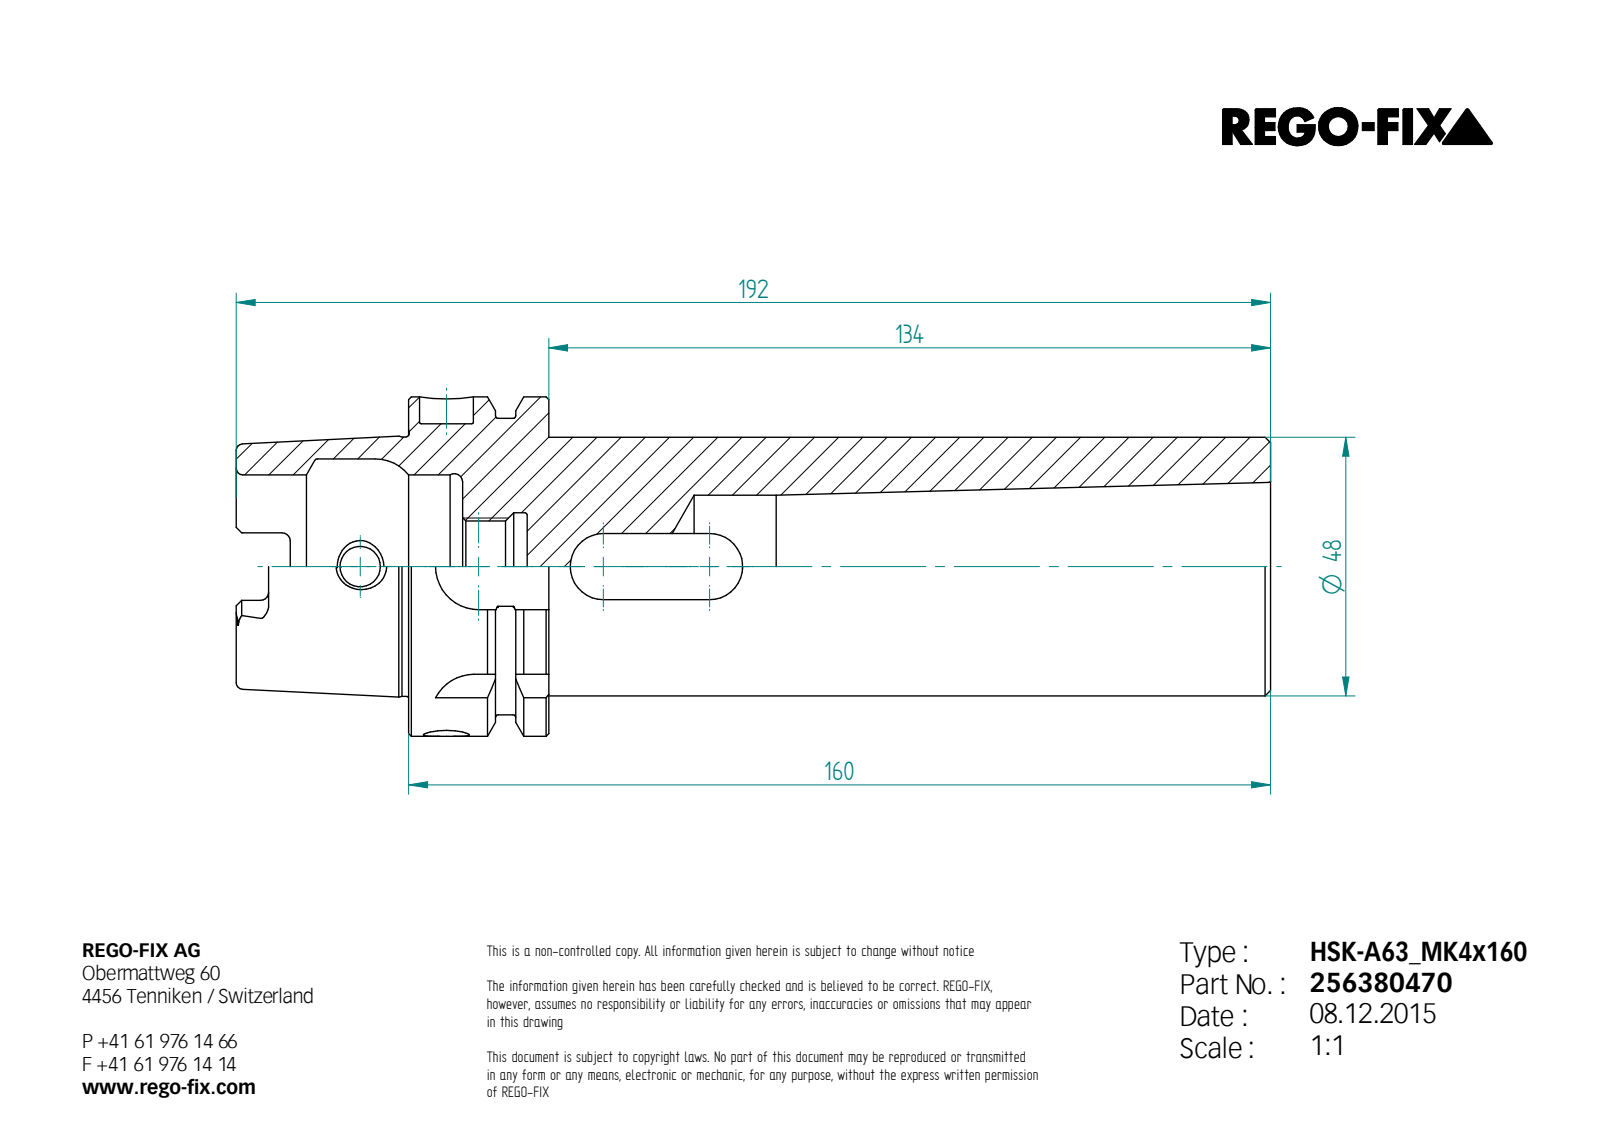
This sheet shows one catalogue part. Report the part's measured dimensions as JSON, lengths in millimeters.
{"step_written_by": "Unknown (AUTOMOTIVE_DESIGN)", "units": "millimeters", "bodies": {"solids": 1, "faces": 129, "planar": 46, "cylindrical": 35, "other": 48}, "overall_size": [192, 63, 63], "volume_mm3": 239944, "surface_area_mm2": 53561, "round_holes": [[7.5, 1], [8.5, 1], [10, 1], [16.92, 1], [20, 1], [26.5, 1], [34, 1], [40, 1]], "round_bosses_or_shafts": [[63, 1], [55, 1], [48.13, 1], [48, 1]], "partial_cylinders_radius": [[1.5, 6], [2.88, 4], [8, 4], [6.15, 2]], "face_to_face_distances": [26, 160, 134, 12.3, 10, 16, 150, 32, 22, 4]}
